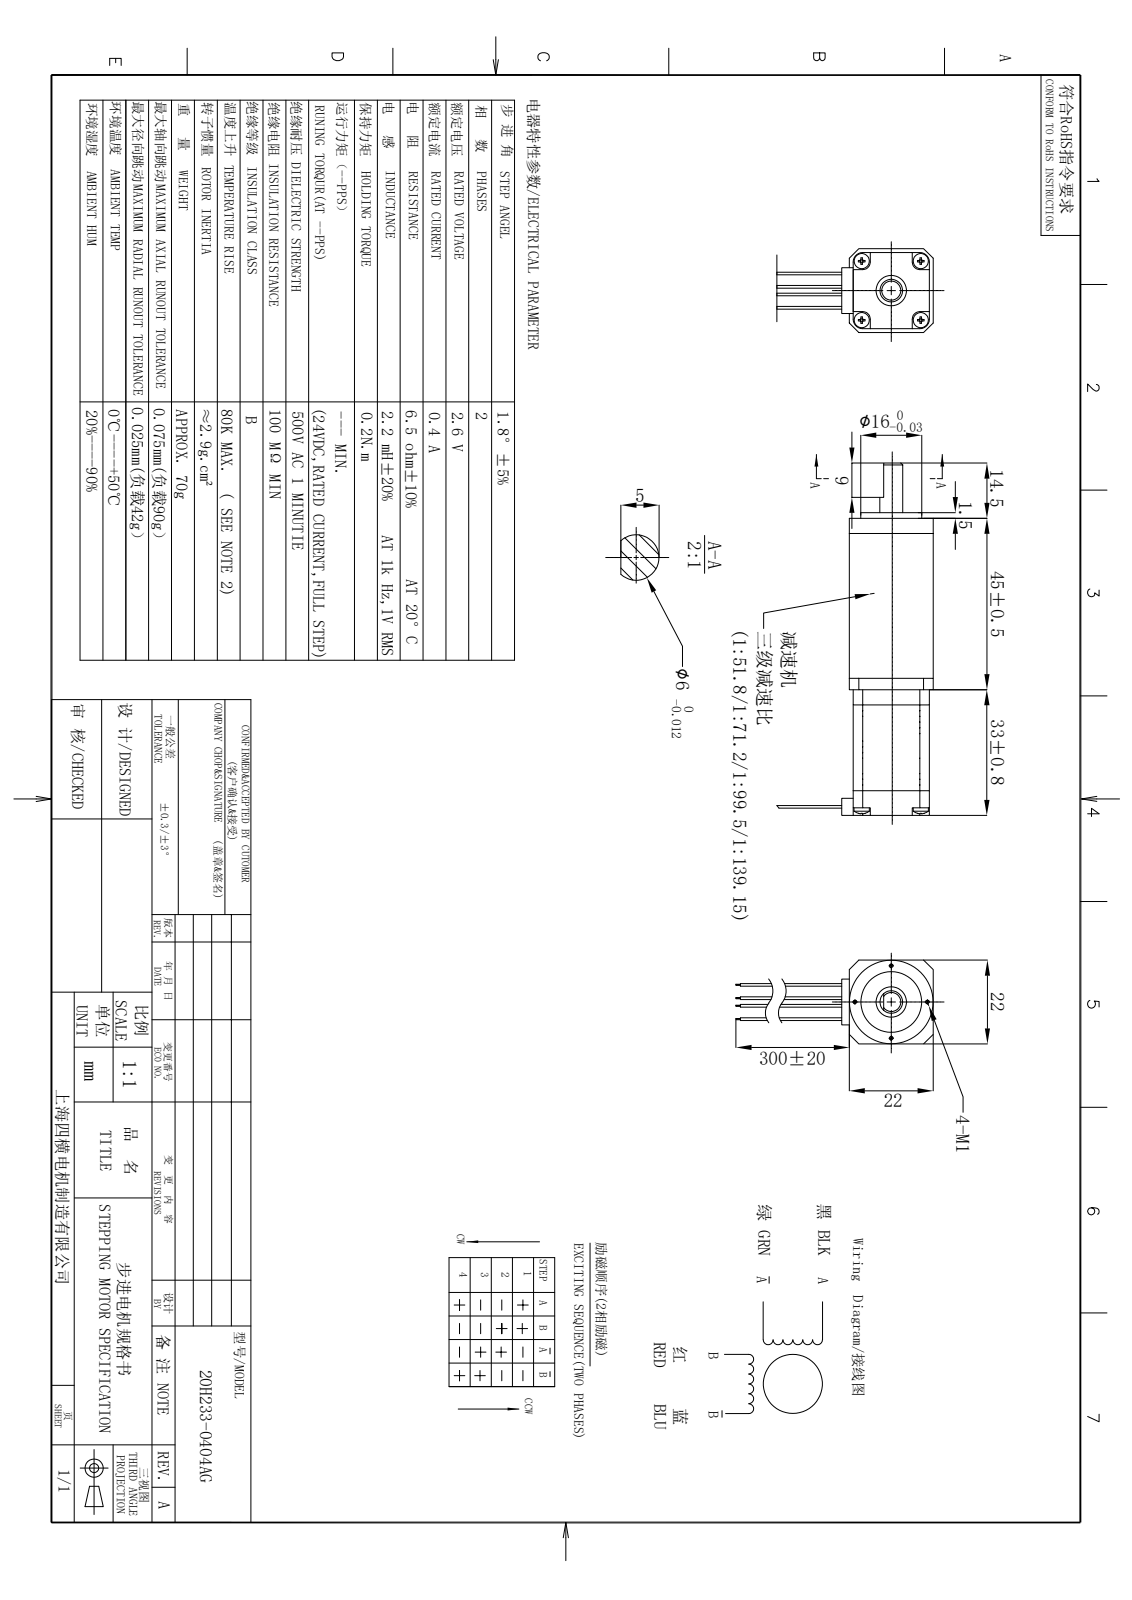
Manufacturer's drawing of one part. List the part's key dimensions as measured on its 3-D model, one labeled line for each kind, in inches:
Part name (STEP PRODUCT): 20H233-0404AG51电机前端盖; 20H233-0404AG51减速器主体; 20H233-0404AG51轴; 20H233-0404AG51减速器前端盖 (+8 more)
STEP written by: SolidWorks 2020 (AUTOMOTIVE_DESIGN)
Units: inches
Bodies: 20 solids, 857 faces (587 planar, 234 cylindrical, 36 other)
Overall size (bounding box): 3.642 × 1.614 × 0.866
Volume: 1.94 in³ · Surface area: 23.17 in²
Round holes (diameter × count): ⌀0.039 ×4, ⌀0.098 ×4, ⌀0.315 ×1
Round bosses / shafts (diameter × count): ⌀0.177 ×4, ⌀0.157 ×4, ⌀0.079 ×4, ⌀0.028 ×4, ⌀0.866 ×1, ⌀0.63 ×1, ⌀0.236 ×1
Partial cylindrical surfaces — rounded edges, fillets, slot ends (radius × count): R0.012 ×16, R0.014 ×4, R0.079 ×4, R0.096 ×4, R0.098 ×4
Main face-to-face distances: 0.787, 0.157, 1.772, 0.118, 1.614, 1.496, 0.276, 0.886, 2.657, 1.043
Hole centre spacings: 0.313, 0.744, 0.374, 0.431, 0.529, 0.61, 0.748, 0.863
